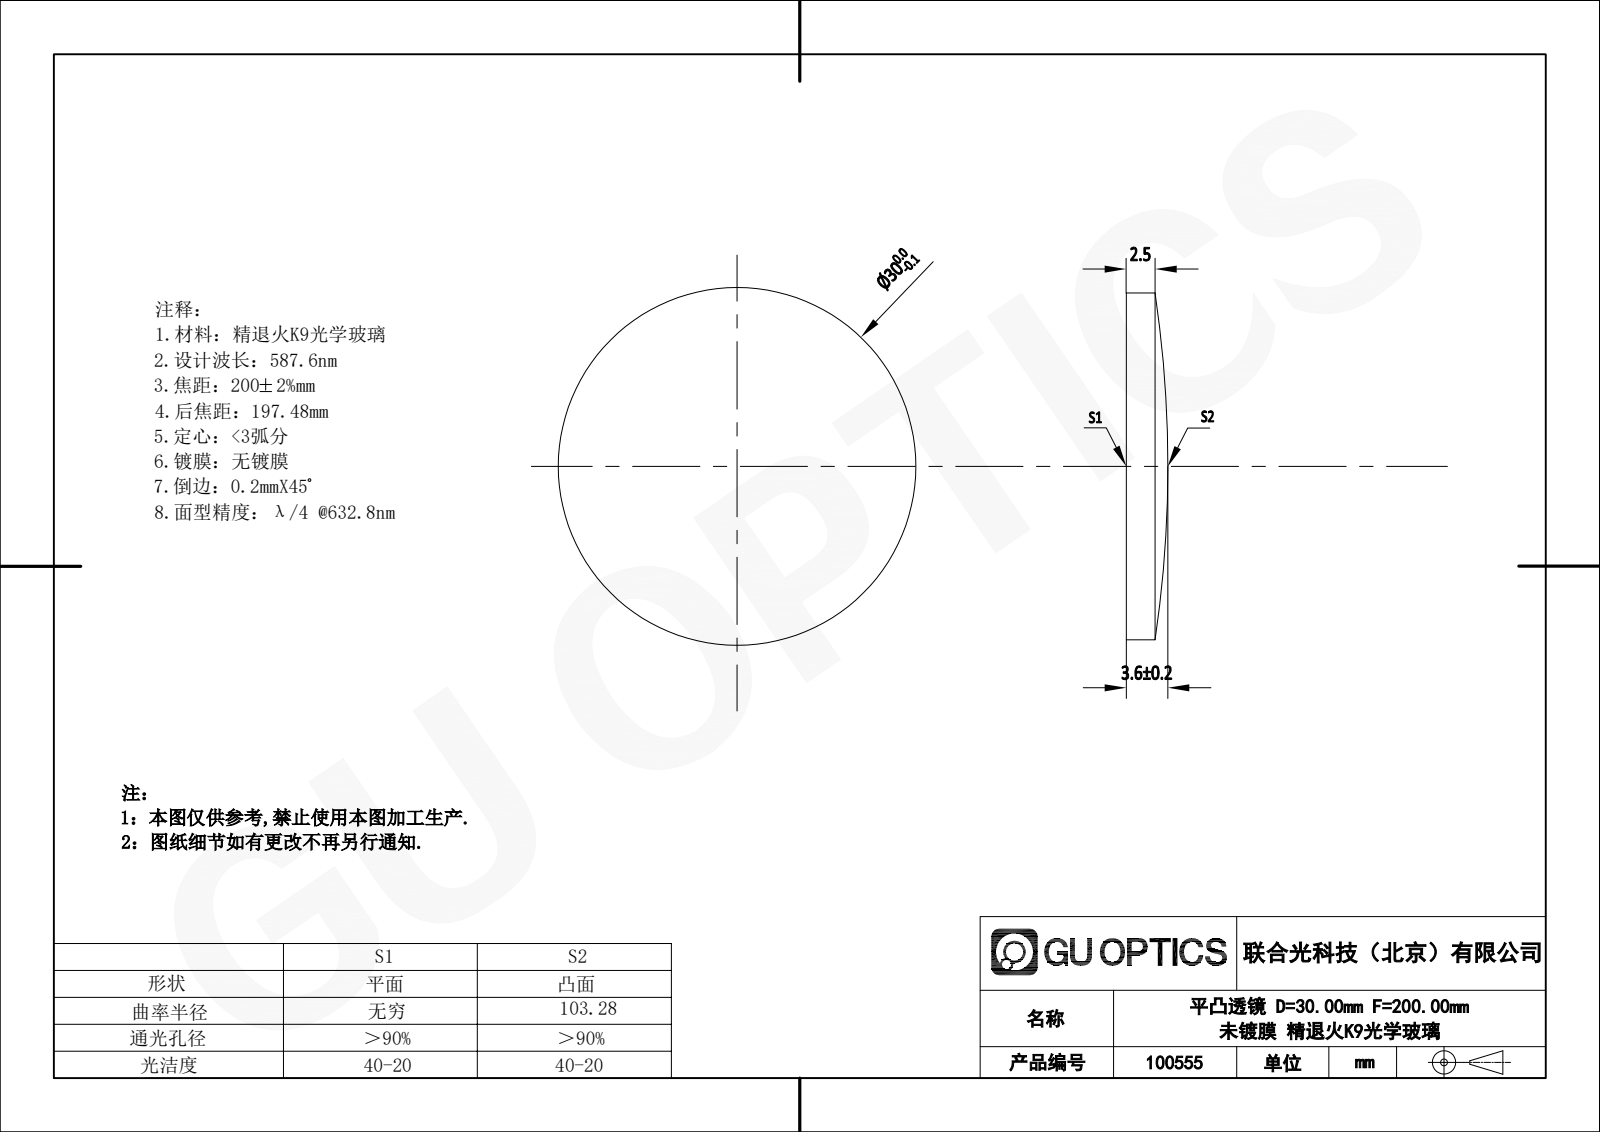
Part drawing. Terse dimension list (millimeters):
name: 100555
written by: SolidWorks 2020 (CONFIG_CONTROL_DESIGN)
unit: mm
bodies: 1 solid, 5 faces (1 planar, 2 cylindrical, 2 other)
size: 30 × 30 × 3.6
volume: 2 156 mm³; area: 1 653 mm²
bosses: 1× ⌀30
